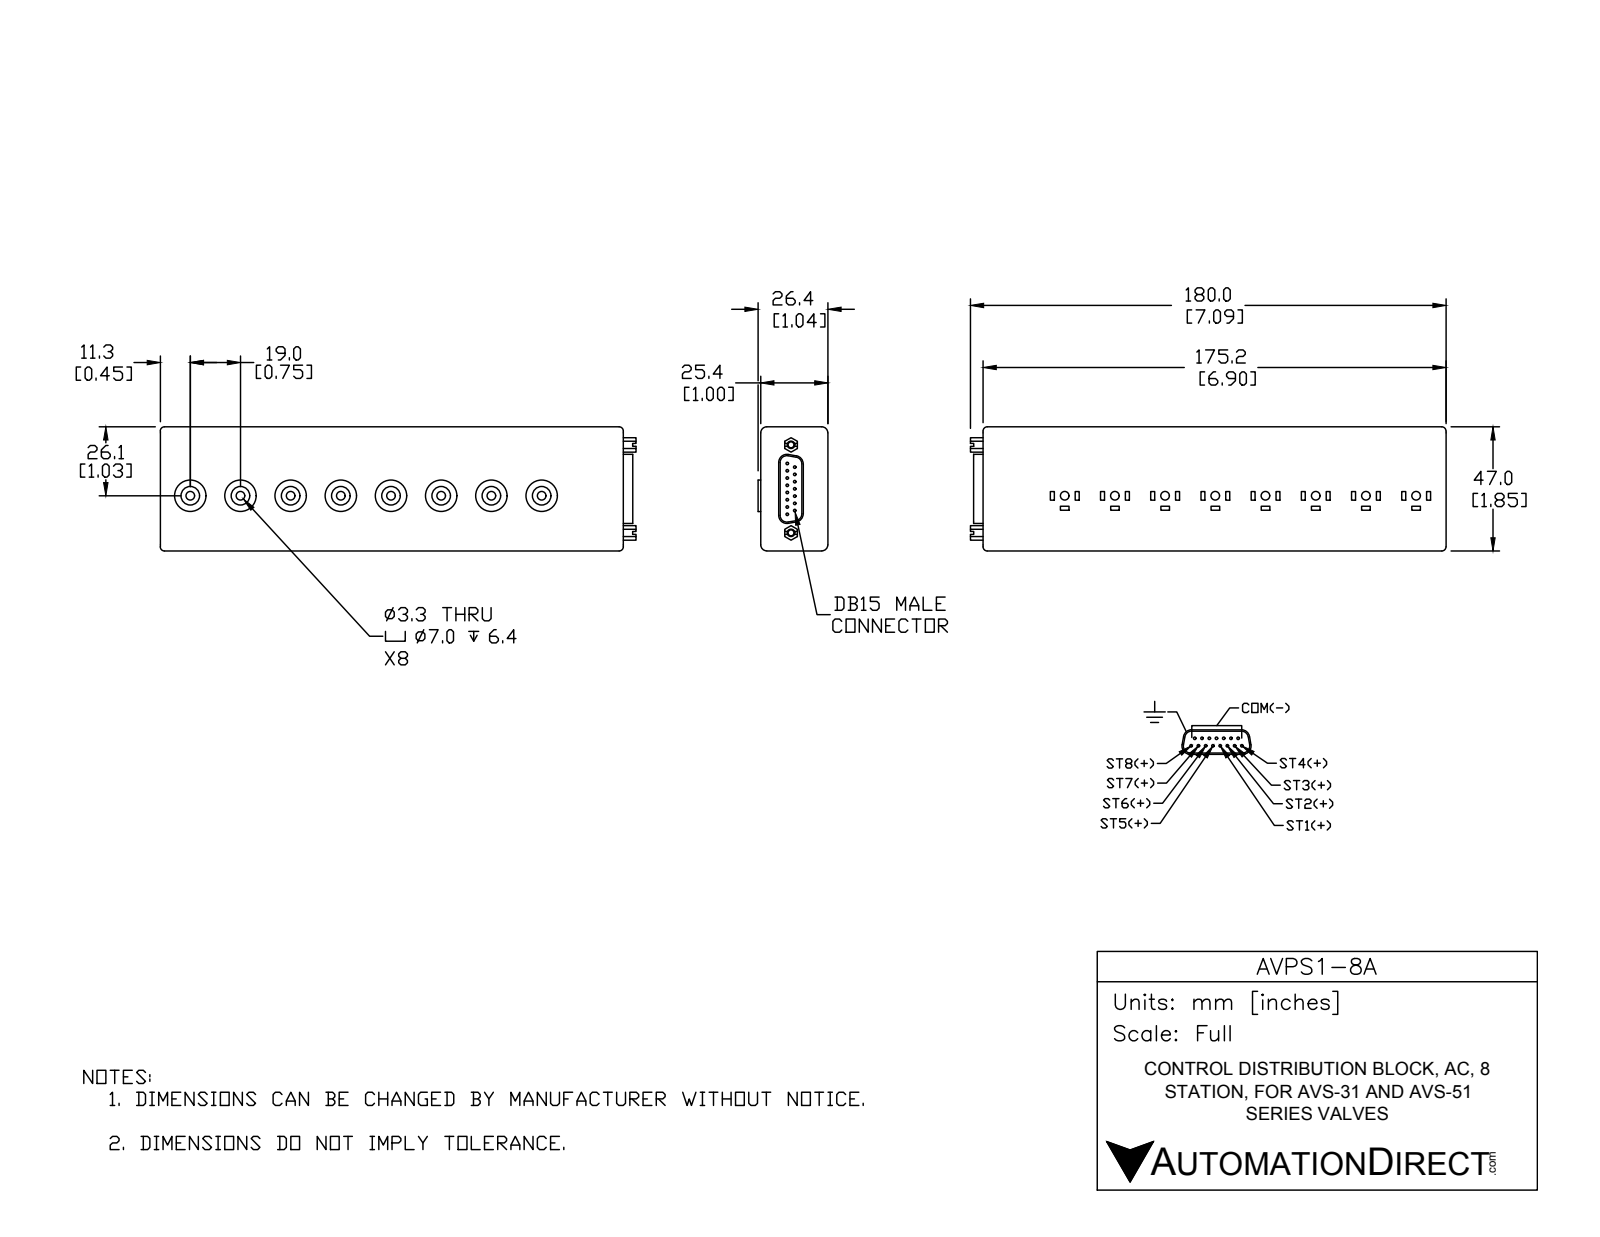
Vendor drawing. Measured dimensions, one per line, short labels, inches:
name: AVPS1-8A
written by: SolidWorks 2016 (AUTOMOTIVE_DESIGN)
unit: in
bodies: 1 solid, 311 faces (195 planar, 104 cylindrical, 12 other)
size: 7.088 × 1.85 × 1.04
volume: 12.5 in³; area: 50.21 in²
holes: 8× ⌀0.13, 8× ⌀0.275, 2× ⌀0.089
bosses: 15× ⌀0.039, 8× ⌀0.469
rounds: 8× R0.062, 4× R0.09, 4× R0.102, 4× R0.122
face distances: 1, 1.85, 6.899, 0.04, 1.04, 0.25, 0.79, 0.059, 0.748, 0.21
hole spacings: 0.748, 1.496, 2.244, 2.992, 3.74, 4.488, 1.311, 5.236
